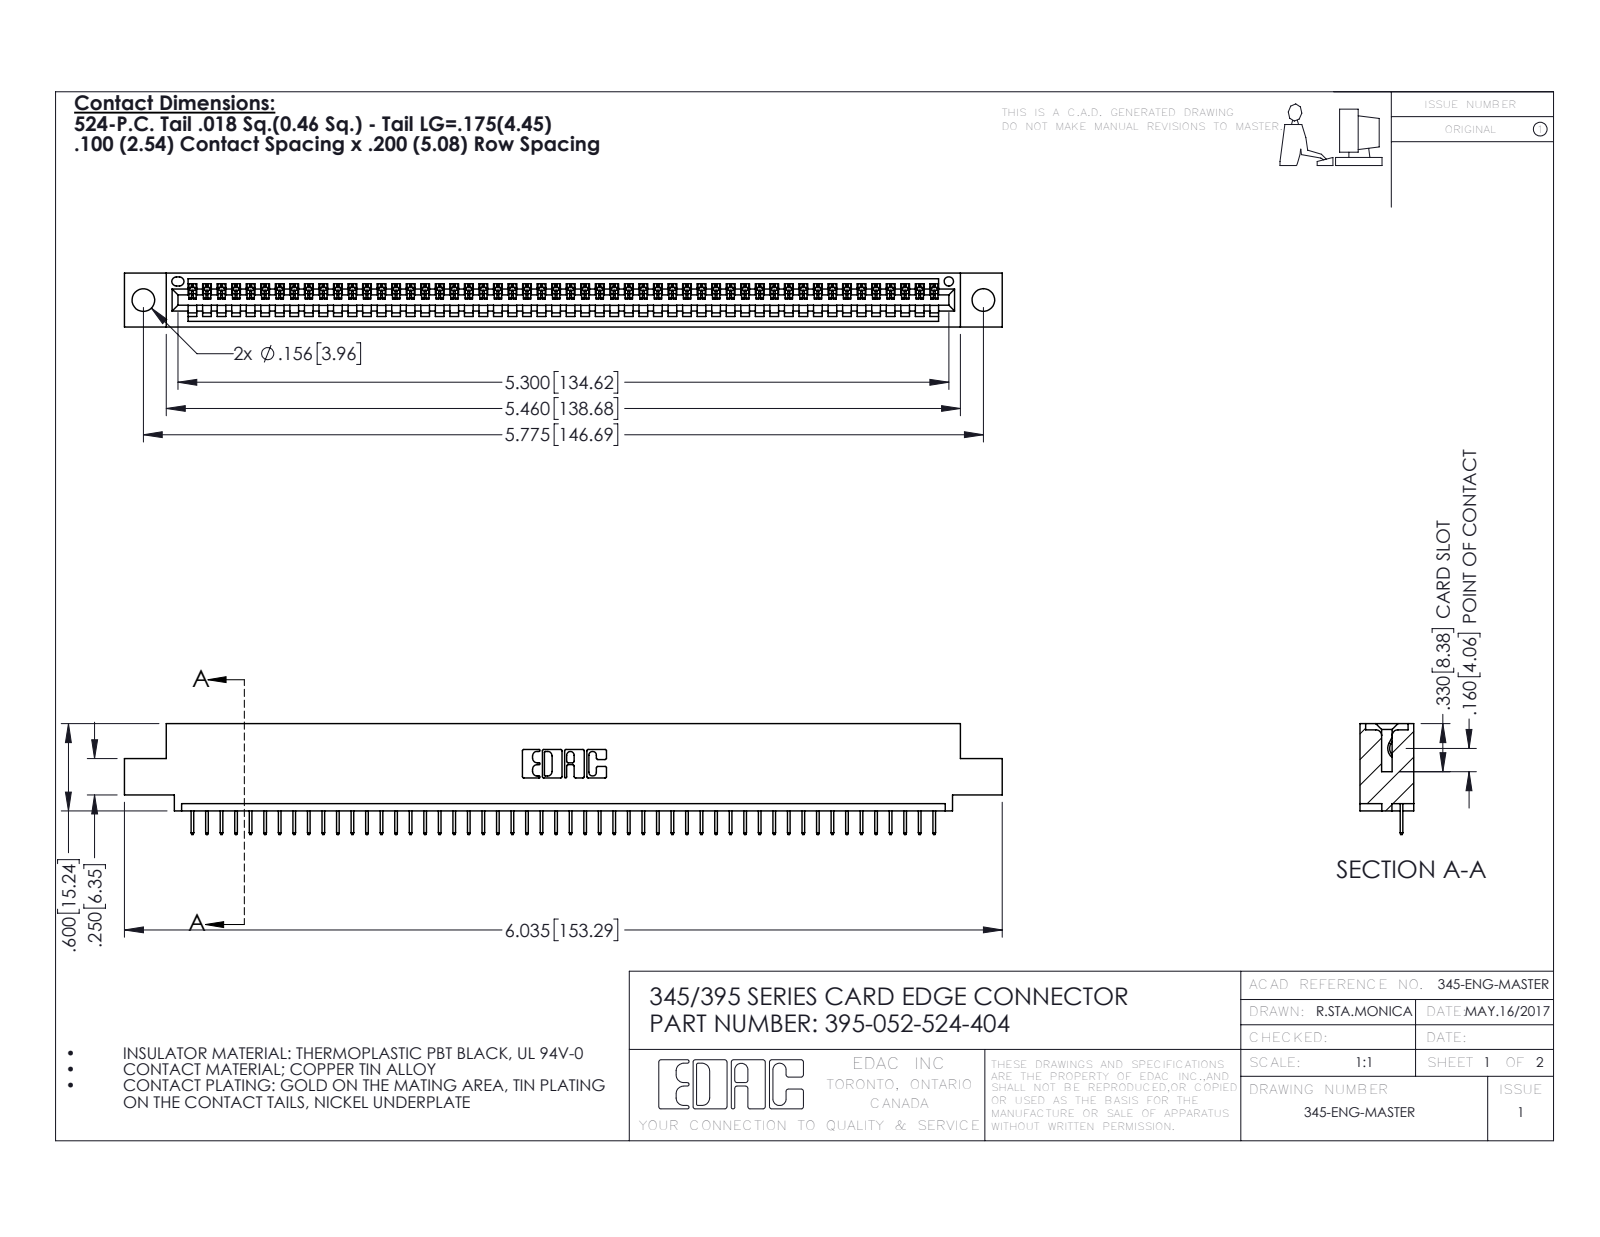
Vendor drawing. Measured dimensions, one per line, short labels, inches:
name: 345-292-001_345-293-124; 345 Part_0.110 Offset - 0.156 Dia-TH; 395-052-524-404
written by: SolidWorks 2016 (CONFIG_CONTROL_DESIGN)
unit: in
bodies: 53 solids, 3354 faces (2476 planar, 878 cylindrical, 0 other)
size: 6.035 × 0.762 × 0.37
volume: 0.871 in³; area: 28.43 in²
holes: 2× ⌀0.156, 1× ⌀0.064
rounds: 104× R0.006, 22× R0.01, 6× R0.007, 6× R0.031, 3× R0.026, 2× R0.031, 2× R0.04, 1× R0.014
face distances: 0.072, 0.298, 0.37, 0.2, 0.098, 0.272, 0.025, 0.225, 0.072, 0.149
hole spacings: 0.27, 5.539, 5.775
